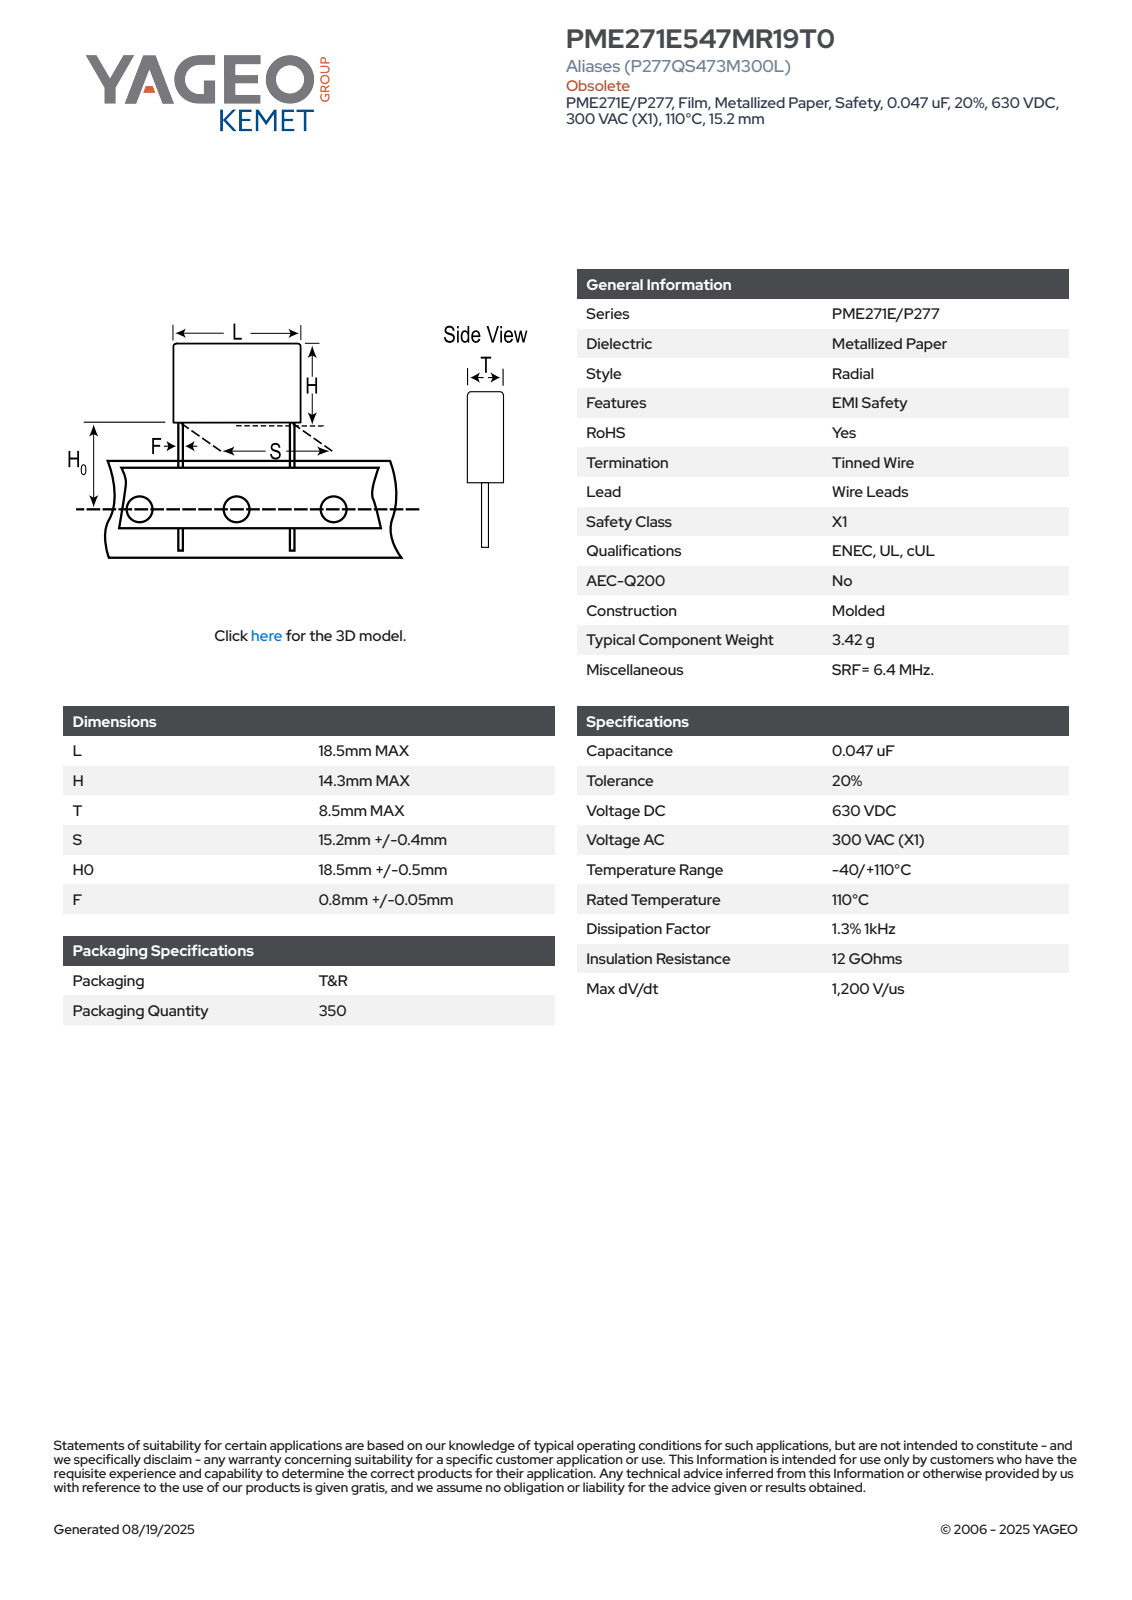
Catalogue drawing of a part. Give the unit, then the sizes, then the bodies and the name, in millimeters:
Units: millimetres
Overall size (bounding box): 33.3 × 18.5 × 8.51
Round bosses / shafts (diameter × count): ⌀0.85 ×2
Partial cylindrical surfaces — rounded edges, fillets, slot ends (radius × count): R0.5 ×4
Main face-to-face distances: 8.5, 14.3, 18.5, 8.51, 19, 33.3, 26.65, 7.65, 6.65, 25
Volume: 2 267 mm³ · Surface area: 1 193 mm²
Bodies: 4 solids, 73 faces (65 planar, 8 cylindrical, 0 other)
Part name (STEP PRODUCT): CFR_MOLDED_18.5X14.3X8.5_L18.5H14.3T8.5S15.2H019F0.85
STEP written by: SolidWorks 2014 (AUTOMOTIVE_DESIGN)
